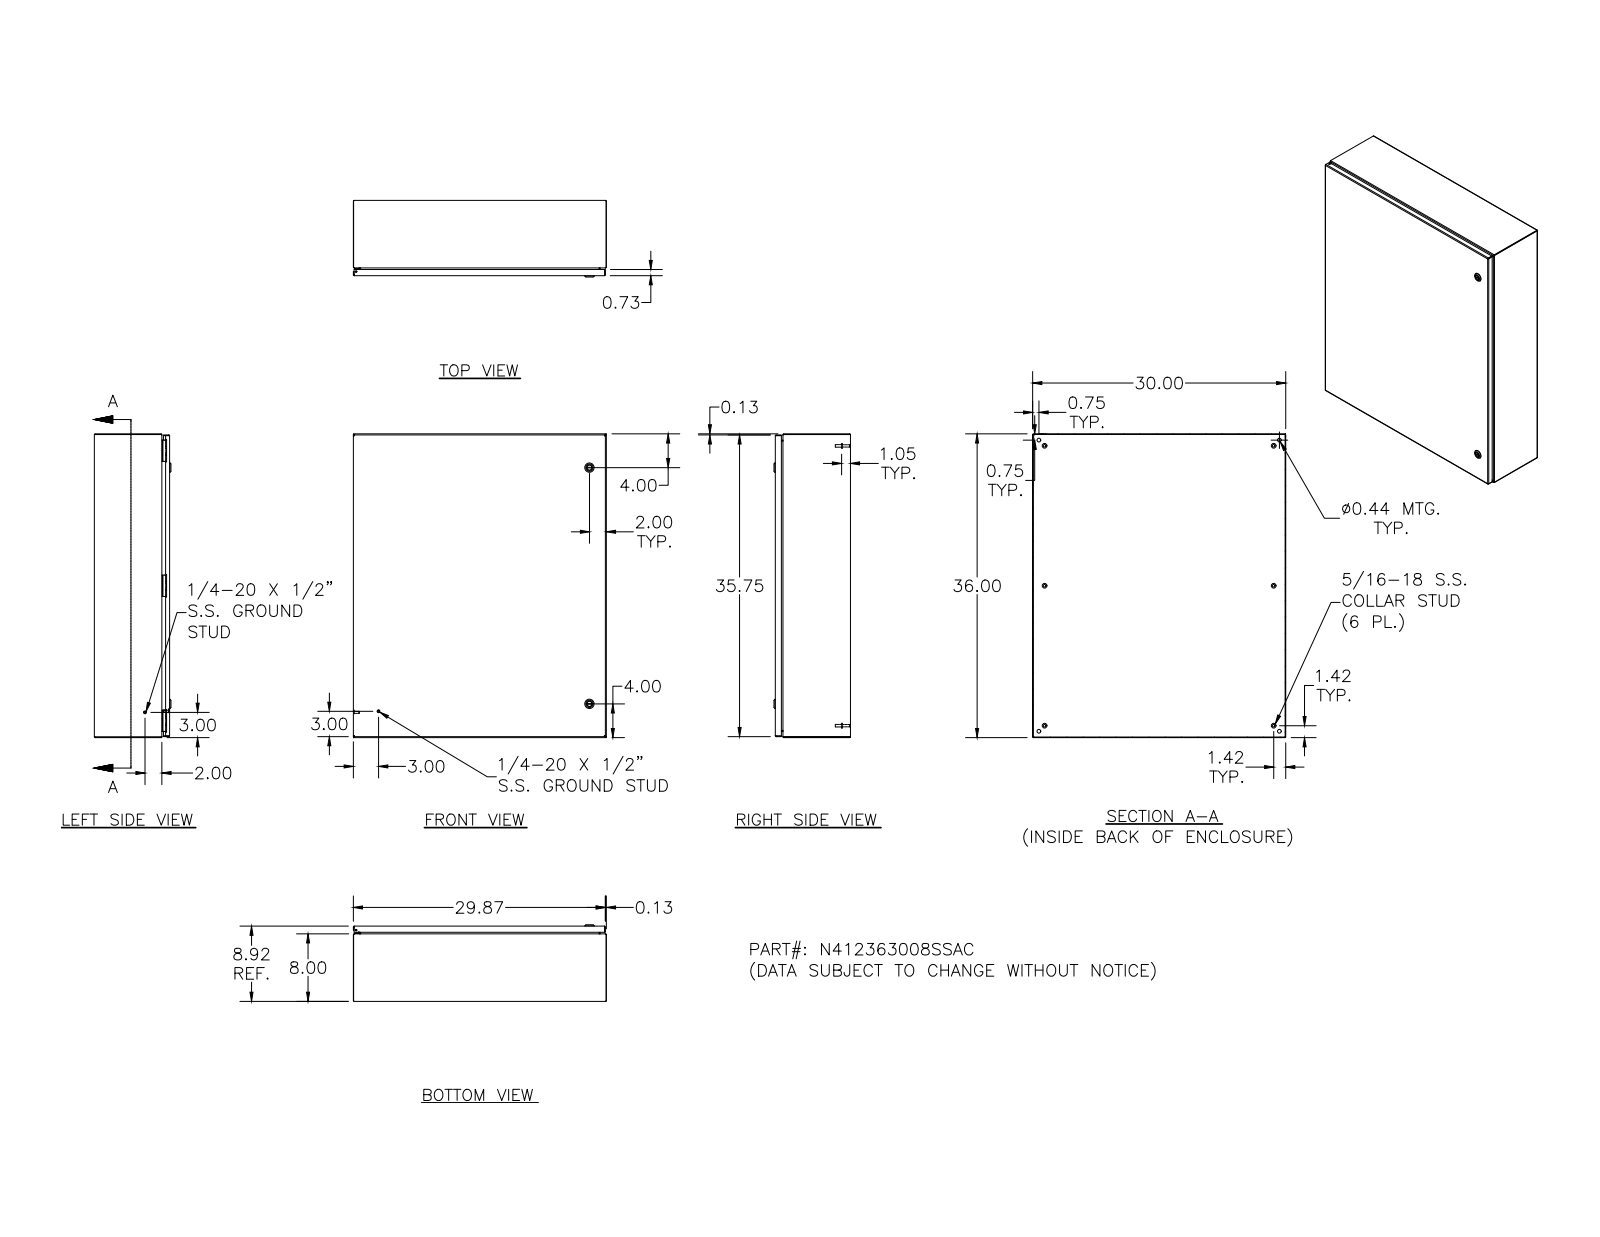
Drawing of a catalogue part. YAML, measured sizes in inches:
part_name: "N412363008SSAC; N412363008SSACBKP; 388151; N4123630SSACLID (+8 more)"
step_written_by: "Autodesk Inventor 2011 (AUTOMOTIVE_DESIGN)"
units: inches
bodies: {solids: 53, faces: 2098, planar: 823, cylindrical: 766, other: 509}
overall_size: [36, 30, 9.075]
volume: 258.6
surface_area: 7014
round_holes:
  - {diameter: 0.188, count: 7}
  - {diameter: 0.093, count: 6}
  - {diameter: 0.152, count: 6}
  - {diameter: 0.167, count: 6}
  - {diameter: 0.172, count: 6}
  - {diameter: 0.437, count: 4}
  - {diameter: 0.156, count: 3}
  - {diameter: 0.197, count: 2}
  - {diameter: 0.315, count: 2}
  - {diameter: 0.394, count: 2}
  - {diameter: 0.402, count: 2}
  - {diameter: 0.634, count: 2}
round_bosses_or_shafts:
  - {diameter: 0.25, count: 14}
  - {diameter: 0.563, count: 6}
  - {diameter: 0.36, count: 6}
  - {diameter: 0.32, count: 6}
  - {diameter: 0.3, count: 6}
  - {diameter: 0.275, count: 6}
  - {diameter: 0.256, count: 6}
  - {diameter: 0.164, count: 6}
partial_cylinders:
  - {radius: 0.05, count: 38}
  - {radius: 0.016, count: 26}
  - {radius: 0.125, count: 21}
  - {radius: 0.031, count: 18}
  - {radius: 0.016, count: 16}
  - {radius: 0.09, count: 16}
  - {radius: 0.02, count: 15}
  - {radius: 0.032, count: 12}
face_to_face_distances: [0.074, 8.843, 8.769, 8.917, 29.926, 35.926, 29.852, 30, 36, 35.852]
hole_center_spacings: [16.004, 32, 15.996, 0.017, 0.66, 15.992, 16, 16.008]
